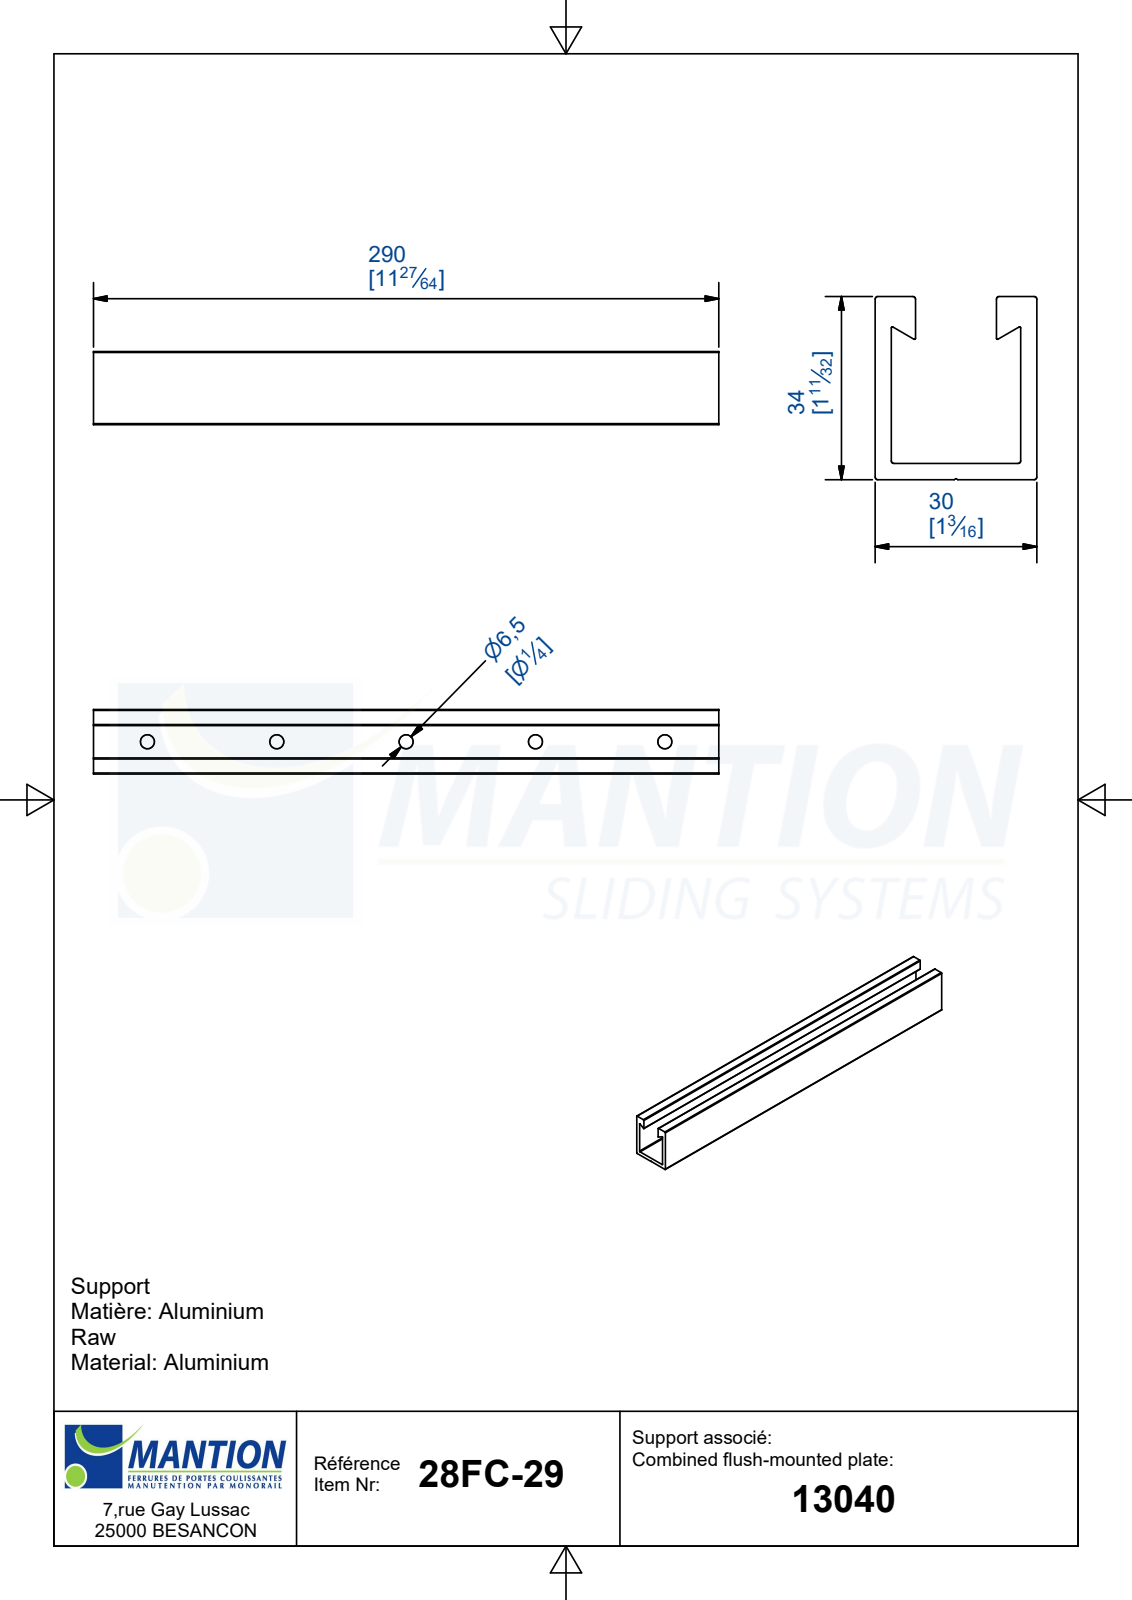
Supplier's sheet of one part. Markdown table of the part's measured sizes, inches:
| quantity | value |
| --- | --- |
| part name | 26153 |
| STEP written by | Autodesk Inventor 2021 (CONFIG_CONTROL_DESIGN) |
| units | inches |
| bodies | 1 solid, 44 faces (27 planar, 17 cylindrical, 0 other) |
| overall size | 11.417 × 1.339 × 1.181 |
| volume | 5.932 in³ |
| surface area | 96.24 in² |
| round holes (diameter × count) | 0.256 × 5 |
| partial cylindrical surfaces (radius × count) | 0.02 × 8, 0.008 × 4 |
| main face-to-face distances | 0.118, 1.063, 1.181, 0.945, 0.295, 0.886, 0.177, 0.768, 1.339, 1.22 |
| hole center spacings | 2.362, 4.724, 7.087, 9.449 |
